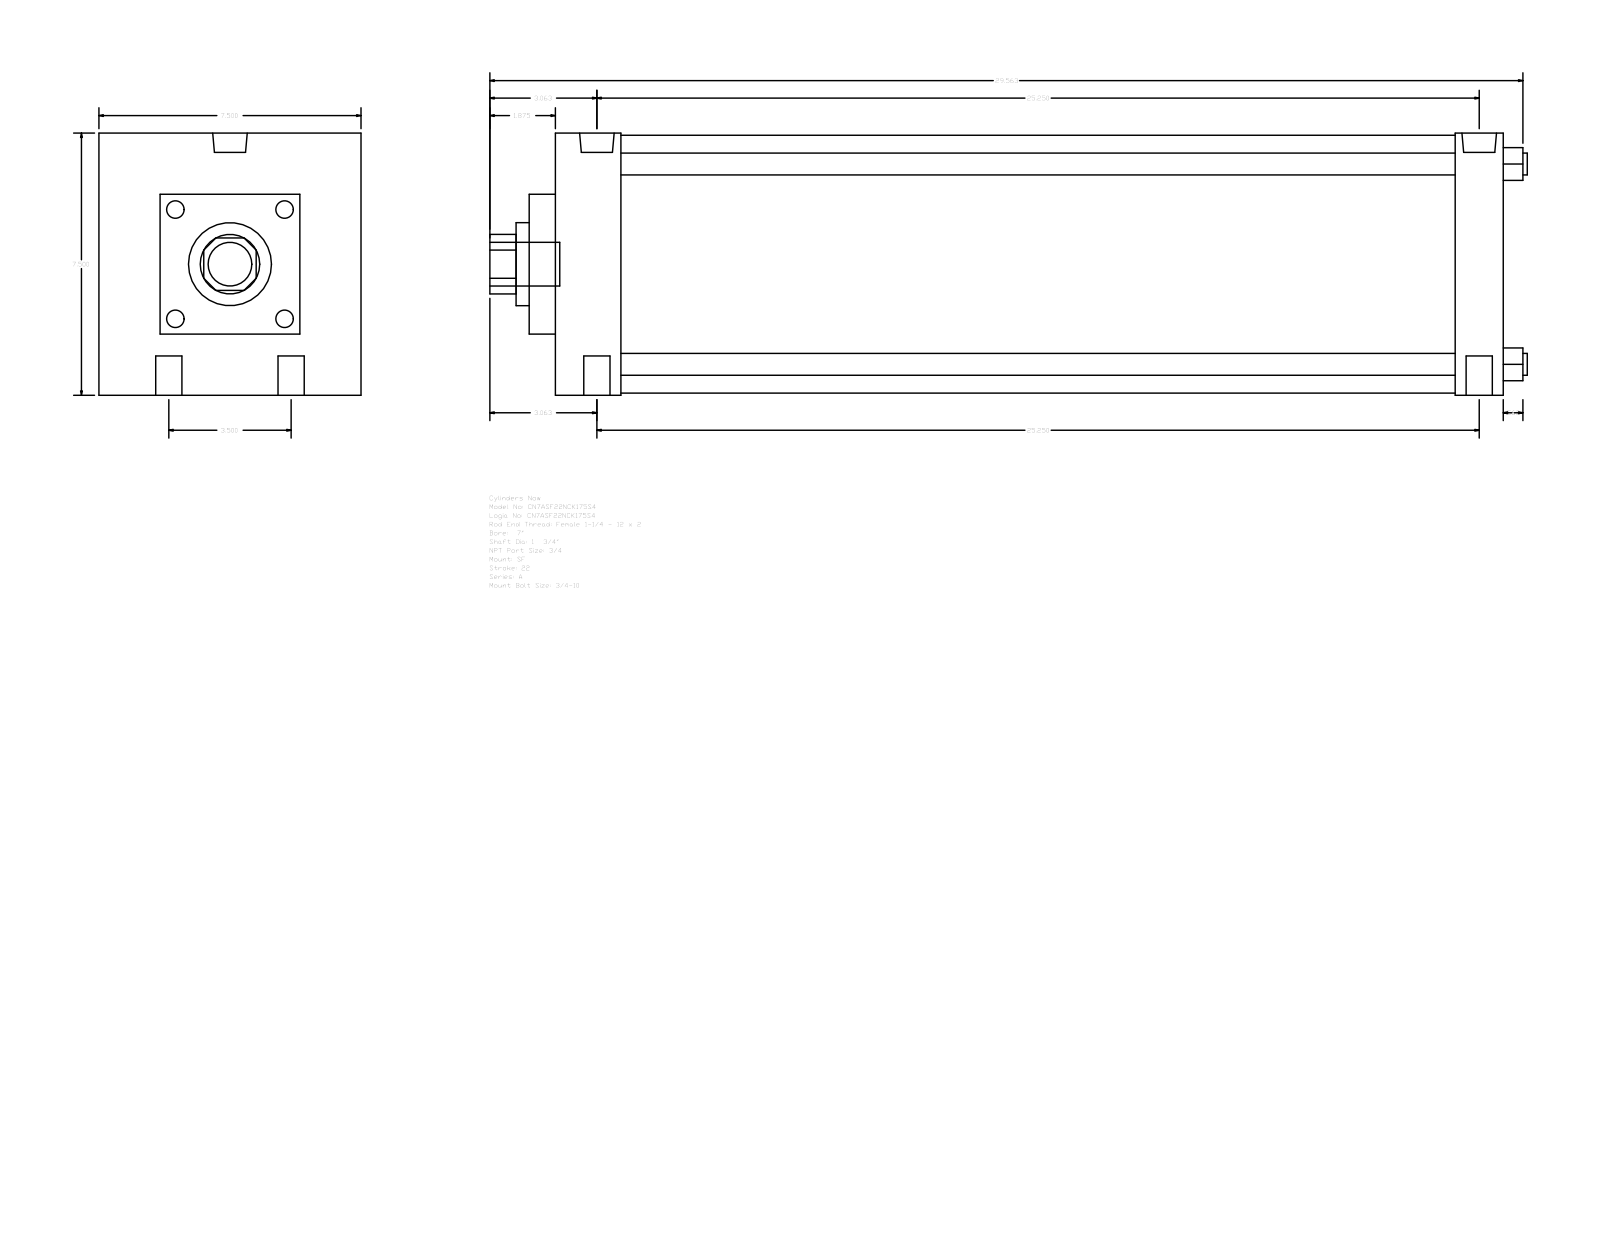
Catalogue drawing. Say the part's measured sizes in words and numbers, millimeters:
The part is named "A_SF__0700_1.75". Its 3-D file was written by "GSSL Pune (CONFIG_CONTROL_DESIGN)". It is 0 solids with 93 faces: 67 planar, 26 cylindrical and 0 other. Overall it measures 754.06 by 190.5 by 190.5 millimeters. Round holes: 4 of diameter 19.05, 2 of diameter 15.08, 2 of diameter 25.12, 1 of diameter 44.45, 1 of diameter 60.33. Round bosses or shafts: 4 of diameter 15.88, 1 of diameter 187.32, 1 of diameter 31.75. Partial cylindrical surfaces (rounded edges, fillets, slot ends): 1 of radius 21.63. The main face-to-face distances are 190.5, 688.98, 44.45, 19.05, 47.63, 654.05, 606.42, 641.35, 34.93, 146.05. The hole center spacings are 44.45, 642.89, 641.35, 88.9, 647.48, 630.23.
